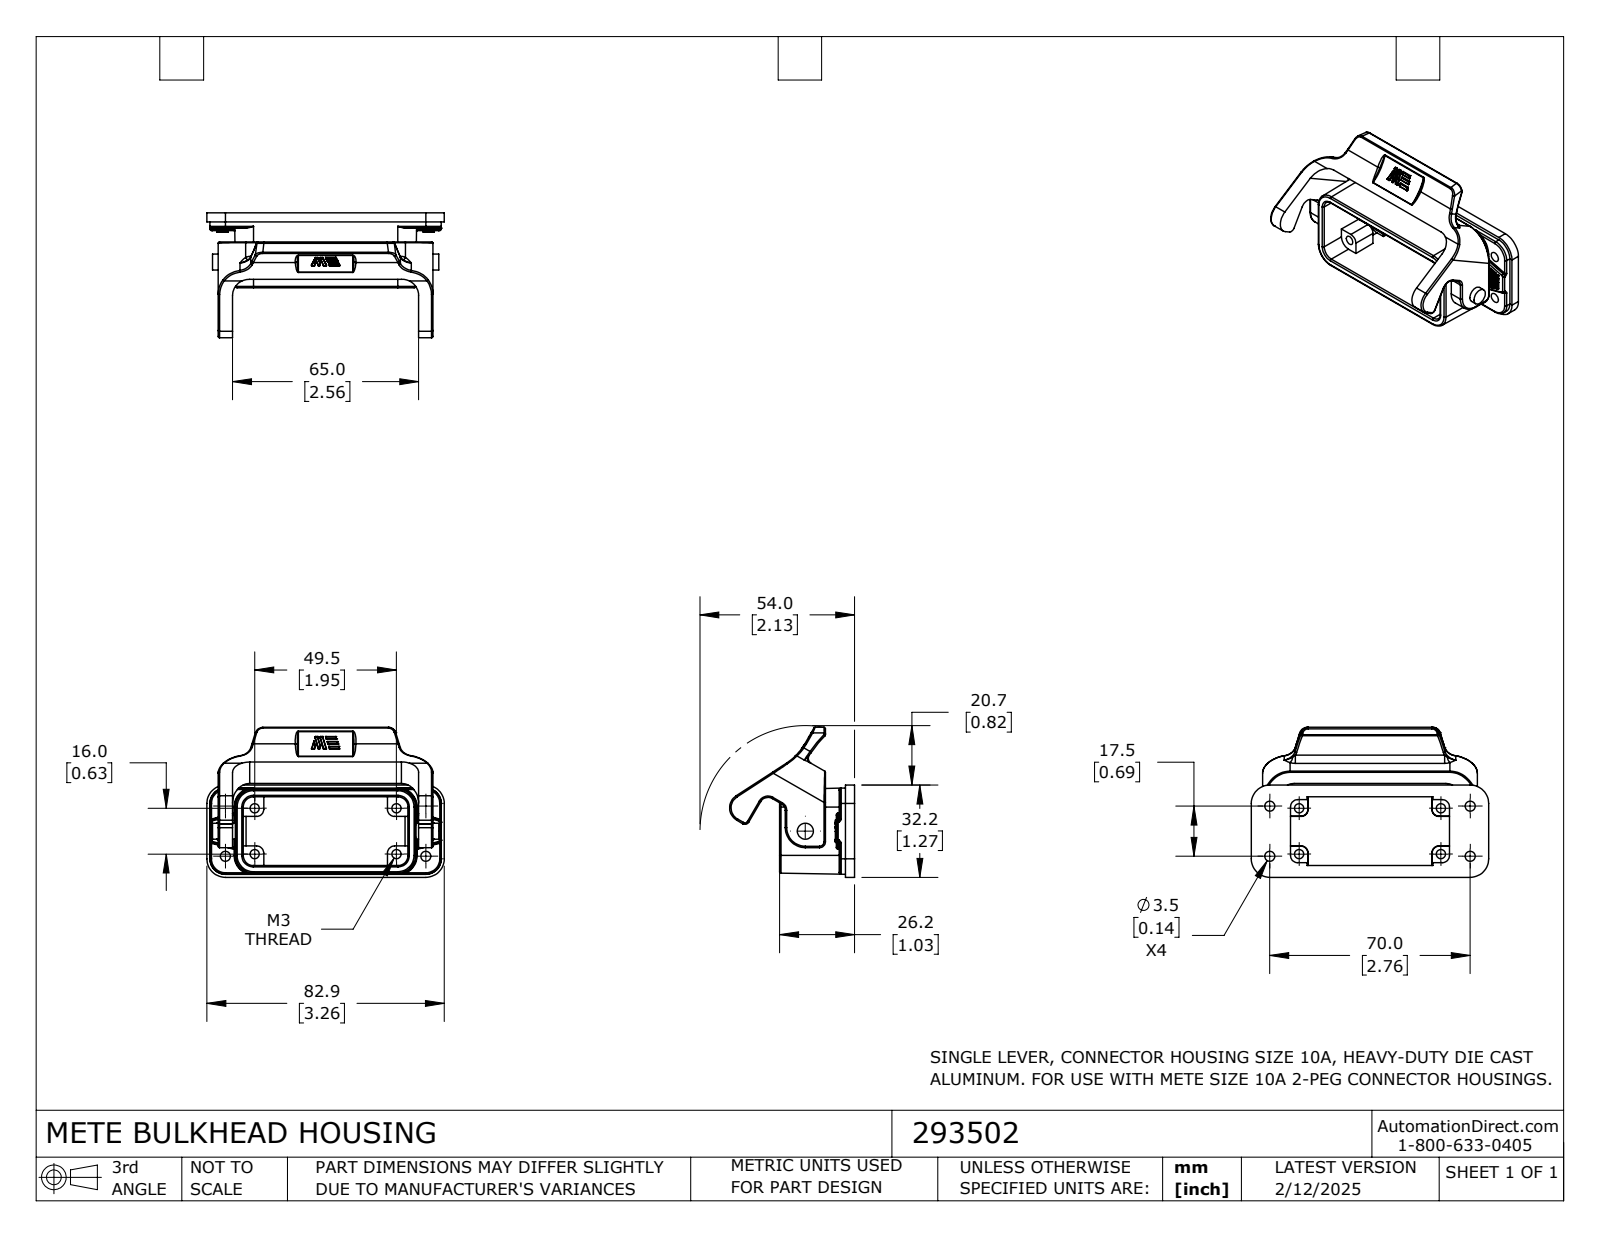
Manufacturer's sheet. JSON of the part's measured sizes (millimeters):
{"part_name": "293502", "step_written_by": "SolidWorks 2024 (CONFIG_CONTROL_DESIGN)", "units": "millimeters", "bodies": {"solids": 1, "faces": 496, "planar": 179, "cylindrical": 207, "other": 110}, "overall_size": [82.9, 52.3, 43.6], "volume_mm3": 28760, "surface_area_mm2": 19090, "round_holes": [[3.2, 4], [3.5, 4]], "round_bosses_or_shafts": [[5.6, 1]], "partial_cylinders_radius": [[0.1, 44], [0.5, 40], [0.2, 12], [2.5, 11], [3.5, 4], [6.5, 4], [5, 3], [1, 2]], "face_to_face_distances": [24, 5, 70, 8.7, 66.2, 3.8, 61.2, 7, 10.2, 4.1], "hole_center_spacings": [10.3, 19.6, 59.7, 62.1, 16, 17.5, 49.5, 52]}
